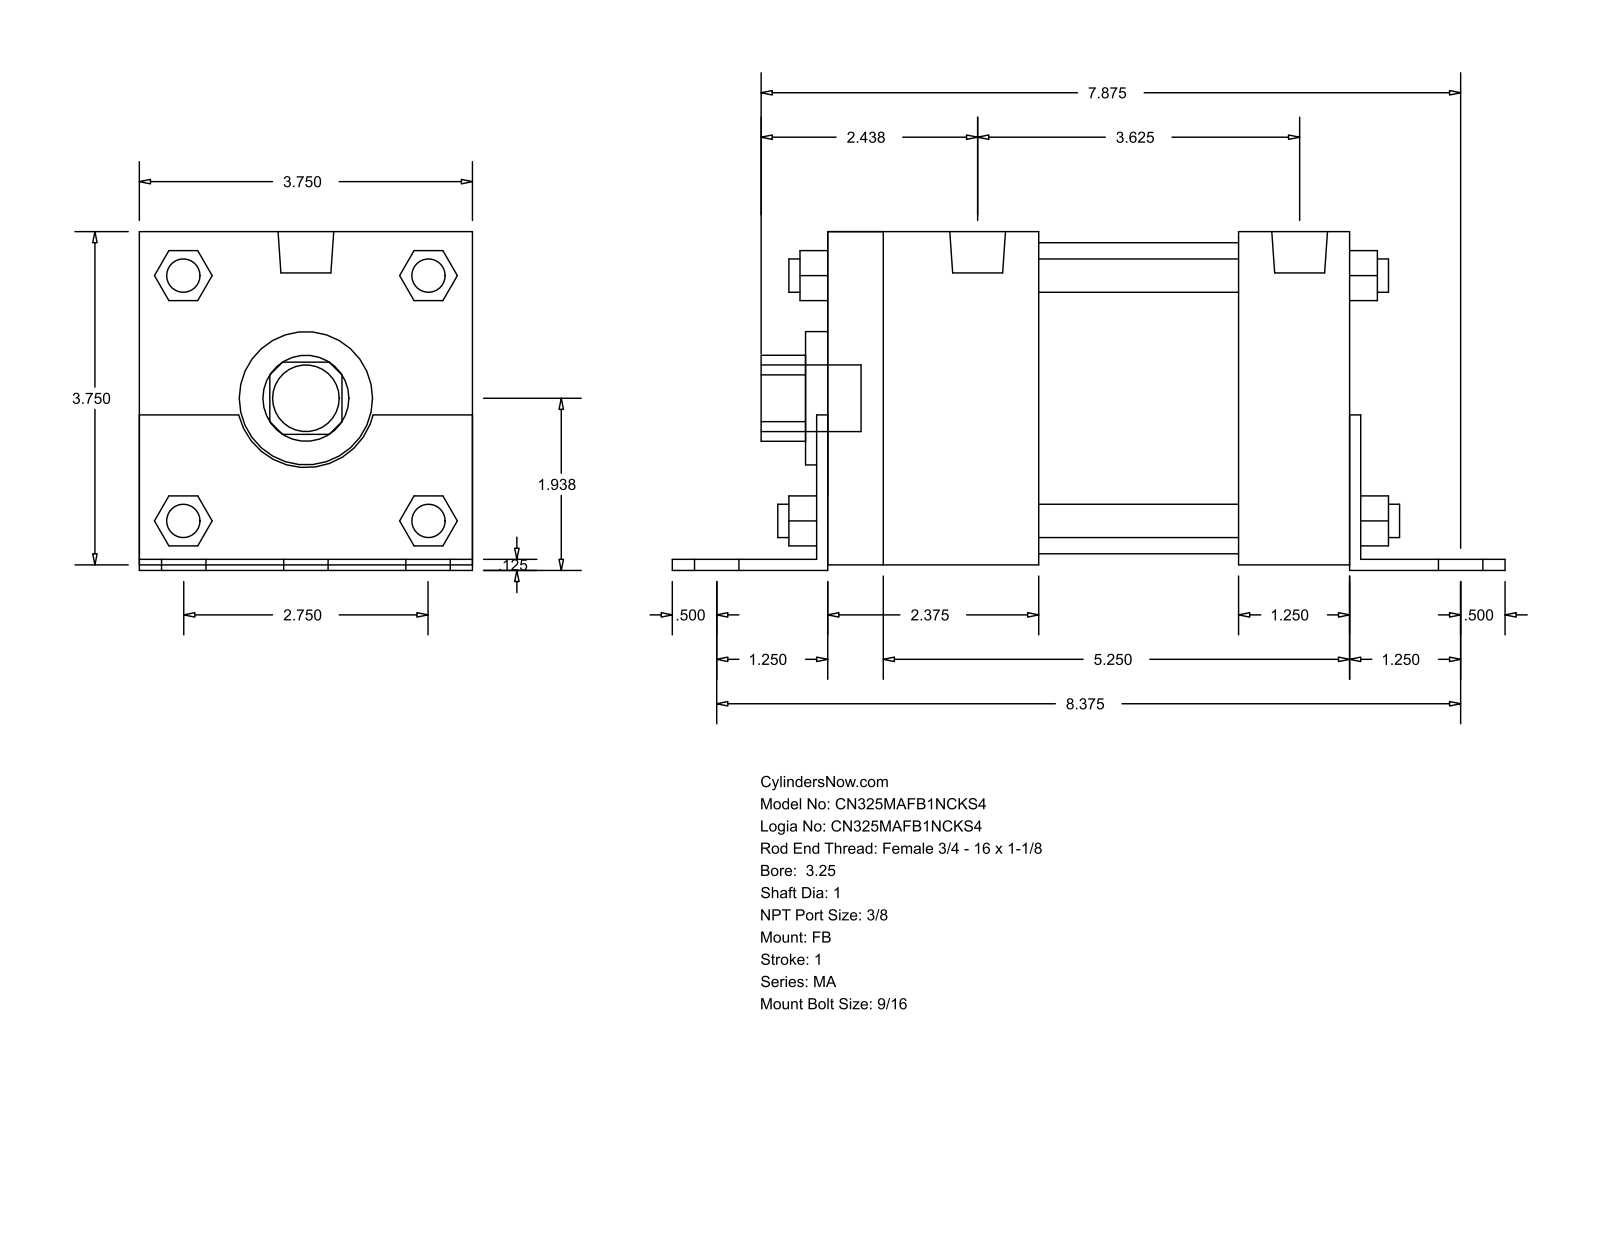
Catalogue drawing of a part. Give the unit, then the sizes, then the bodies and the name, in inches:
Units: inches
Overall size (bounding box): 9.375 × 3.813 × 3.75
Round holes (diameter × count): ⌀1 ×1, ⌀1.5 ×1, ⌀3.5 ×1
Round bosses / shafts (diameter × count): ⌀0.563 ×6, ⌀0.437 ×4, ⌀0.375 ×4, ⌀0.627 ×2, ⌀0.75 ×1
Partial cylindrical surfaces — rounded edges, fillets, slot ends (radius × count): R0.484 ×1, R0.78 ×1
Main face-to-face distances: 3.75, 0.125, 0.063, 3.812, 0.062, 3.687, 6, 5.875, 6.125, 4.75
Bodies: 0 solids, 140 faces (105 planar, 35 cylindrical, 0 other)
Part name (STEP PRODUCT): MA_FB__0325_1
STEP written by: GSSL Pune (CONFIG_CONTROL_DESIGN)
